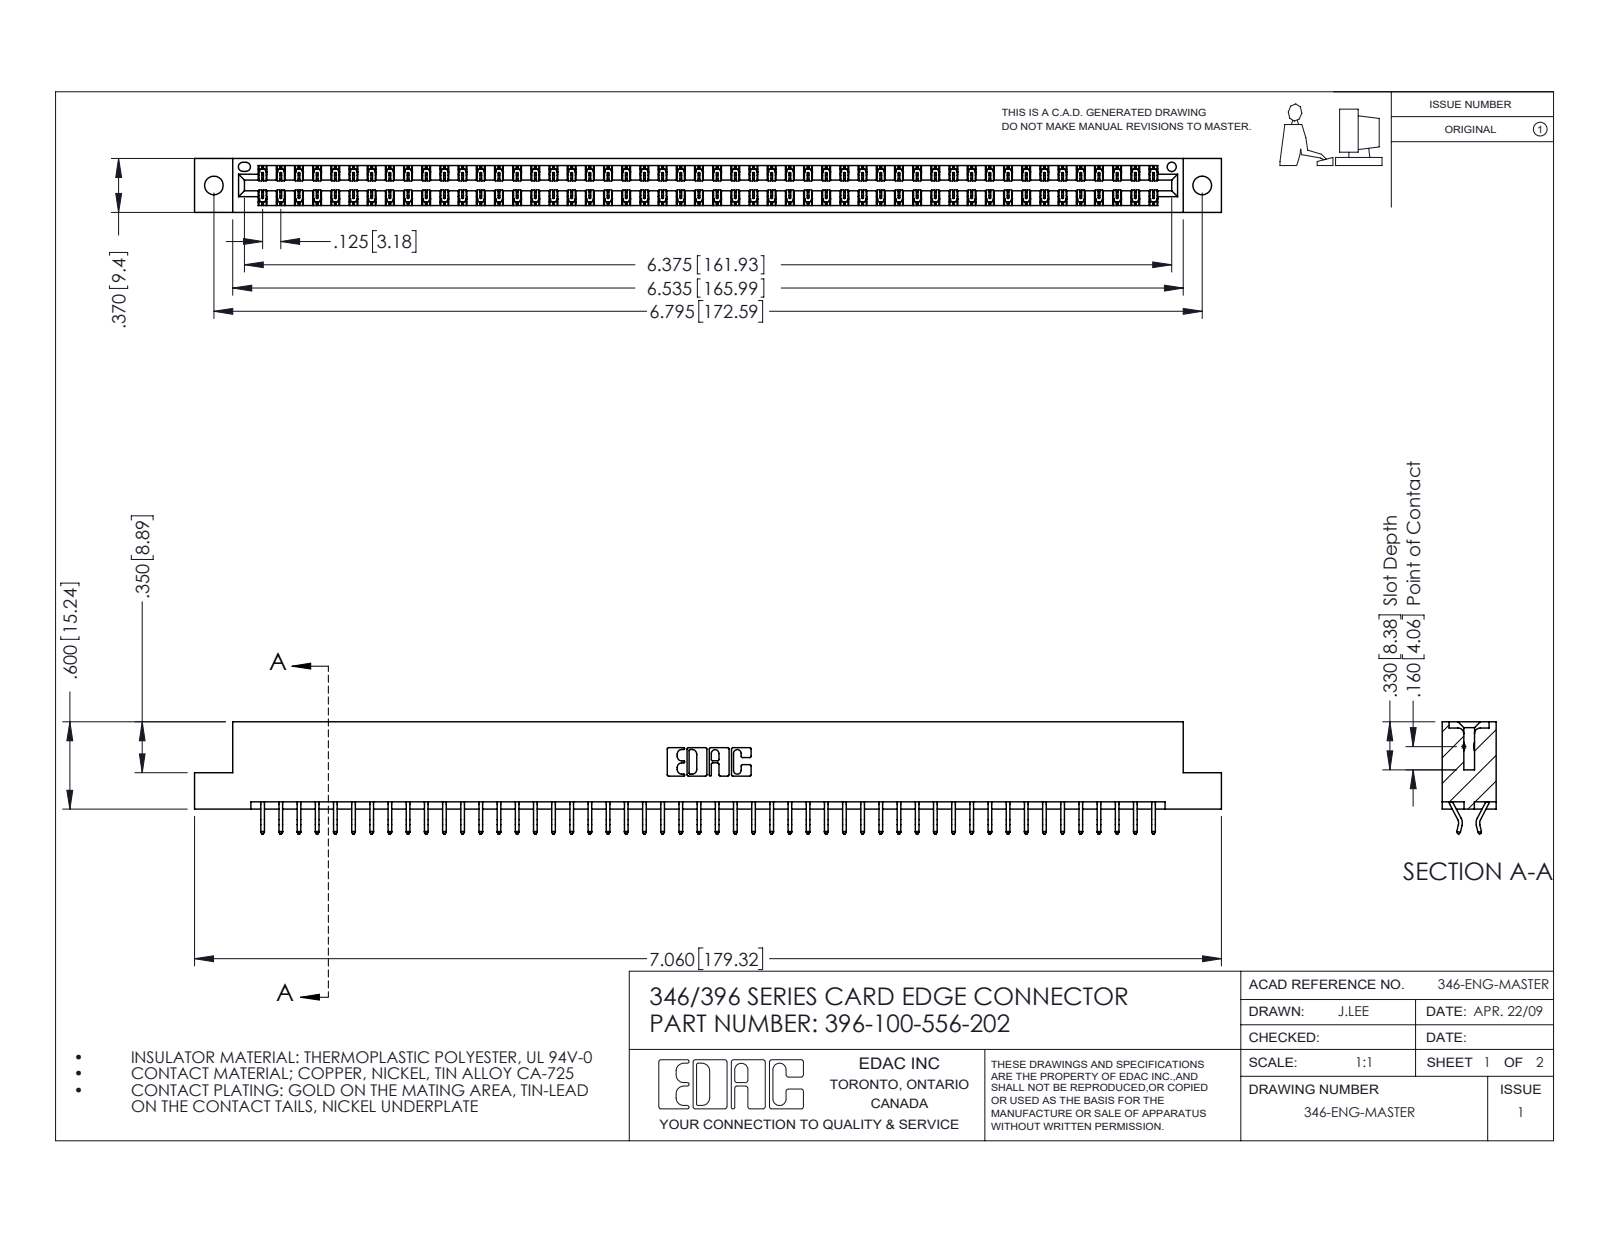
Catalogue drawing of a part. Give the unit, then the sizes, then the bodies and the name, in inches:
Units: inches
Overall size (bounding box): 7.06 × 0.77 × 0.37
Round holes (diameter × count): ⌀0.128 ×2, ⌀0.064 ×1
Partial cylindrical surfaces — rounded edges, fillets, slot ends (radius × count): R0.006 ×150, R0.01 ×22, R0.007 ×6, R0.031 ×6, R0.026 ×3, R0.01 ×2, R0.014 ×2, R0.022 ×2
Main face-to-face distances: 0.048, 0.322, 0.37, 0.25, 0.025, 0.072, 0.298, 0.275, 0.148, 0.222
Hole centre spacings: 0.246, 6.586, 6.795
Volume: 1.068 in³ · Surface area: 36.94 in²
Bodies: 101 solids, 5922 faces (3976 planar, 1946 cylindrical, 0 other)
Part name (STEP PRODUCT): 345-292-001_556 Tail; 396-100-556-202; 346 Part_Flush Mounting Lugs - 0.128 Dia
STEP written by: SolidWorks 2016 (CONFIG_CONTROL_DESIGN)
